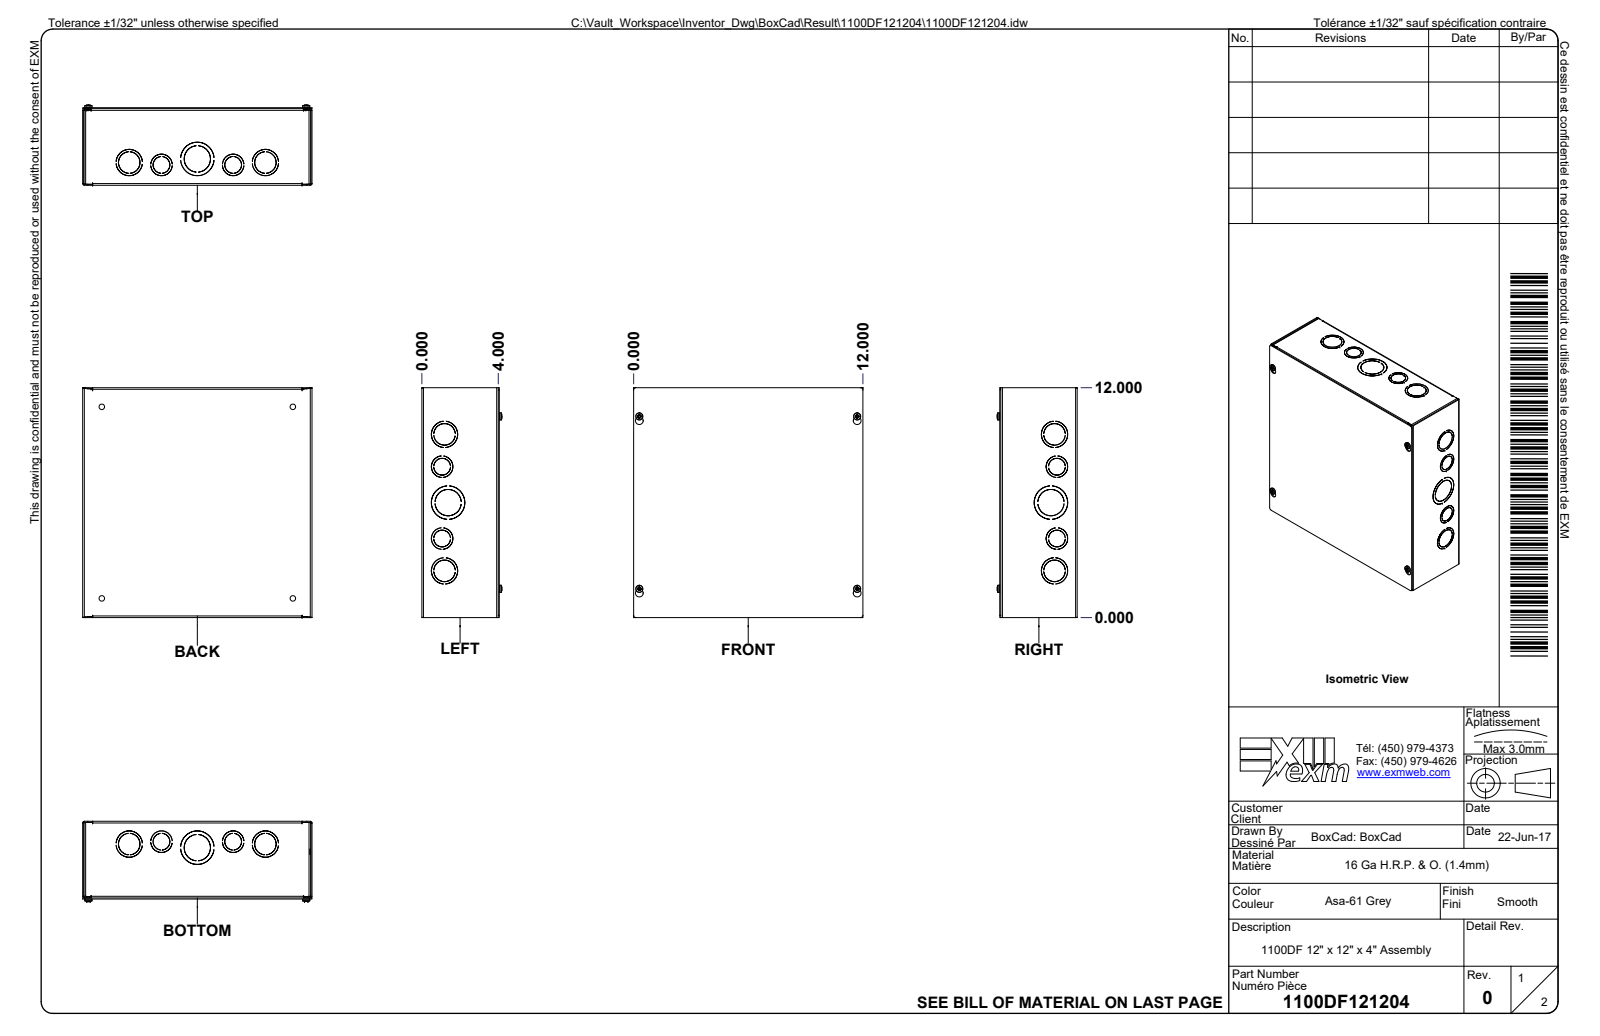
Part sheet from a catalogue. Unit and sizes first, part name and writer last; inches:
Units: inches
Overall size (bounding box): 12 × 12 × 4.183
Round holes (diameter × count): ⌀0.165 ×8, ⌀1.125 ×8, ⌀1.375 ×6, ⌀0.29 ×4, ⌀0.406 ×4, ⌀0.875 ×4, ⌀0.033 ×2, ⌀0.177 ×2, ⌀1.75 ×2, ⌀0.043 ×1, ⌀0.312 ×1, ⌀1.063 ×1
Round bosses / shafts (diameter × count): ⌀1.125 ×8, ⌀1.375 ×6, ⌀0.875 ×4, ⌀0.374 ×4, ⌀1.75 ×2, ⌀0.03 ×2, ⌀1.25 ×1, ⌀1.142 ×1
Partial cylindrical surfaces — rounded edges, fillets, slot ends (radius × count): R0.004 ×28, R0.031 ×14, R0.086 ×14, R0.059 ×12, R0.11 ×12, R0.062 ×4, R0.094 ×4, R0.117 ×4
Main face-to-face distances: 0.055, 11.945, 3.945, 0.053, 4, 4.053, 3.998, 12, 11.89, 3.89
Hole centre spacings: 0.86, 9.526, 10.27, 10.712, 14.309, 9, 11.4, 14.524
Volume: 27.34 in³ · Surface area: 1 032 in²
Bodies: 8 solids, 3585 faces (2178 planar, 515 cylindrical, 892 other)
Part name (STEP PRODUCT): 1100DF121204; 1100DF121204B; 1100DF121204B-P; 1100DF121204C (+5 more)
STEP written by: Autodesk Inventor 2024 (AUTOMOTIVE_DESIGN)
